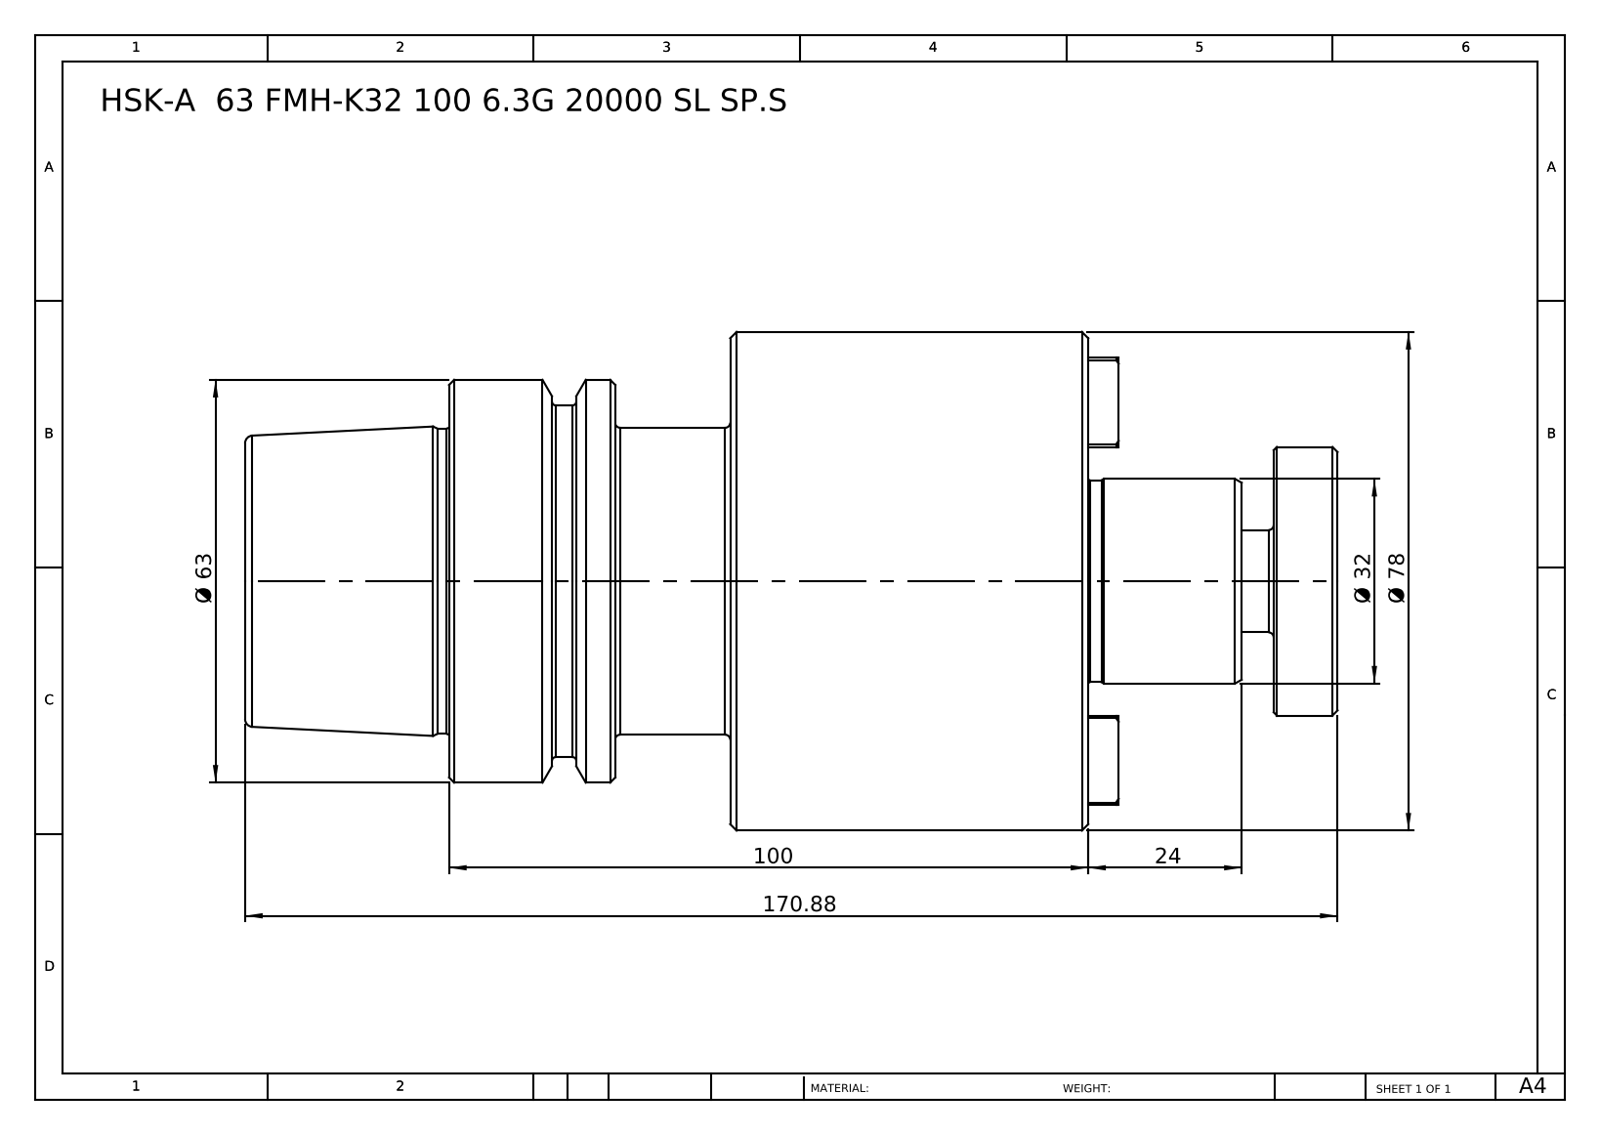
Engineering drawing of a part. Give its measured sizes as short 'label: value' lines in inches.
name: HSK-A 63 FMH32 100 6.3G 20000 SL SP.S
written by: SolidWorks 2014 (CONFIG_CONTROL_DESIGN)
unit: in
bodies: 1 solid, 100 faces (36 planar, 20 cylindrical, 44 other)
size: 6.728 × 3.071 × 3.071
volume: 28.59 in³; area: 70.14 in²
bosses: 1× ⌀3.071, 1× ⌀2.48, 1× ⌀2.165, 1× ⌀1.89, 1× ⌀1.881, 1× ⌀1.654, 1× ⌀1.26, 1× ⌀1.244
face distances: 2.205, 5.192, 2.987, 1.535, 3.74, 6.728, 0.394, 1.142, 3.346, 6.334
